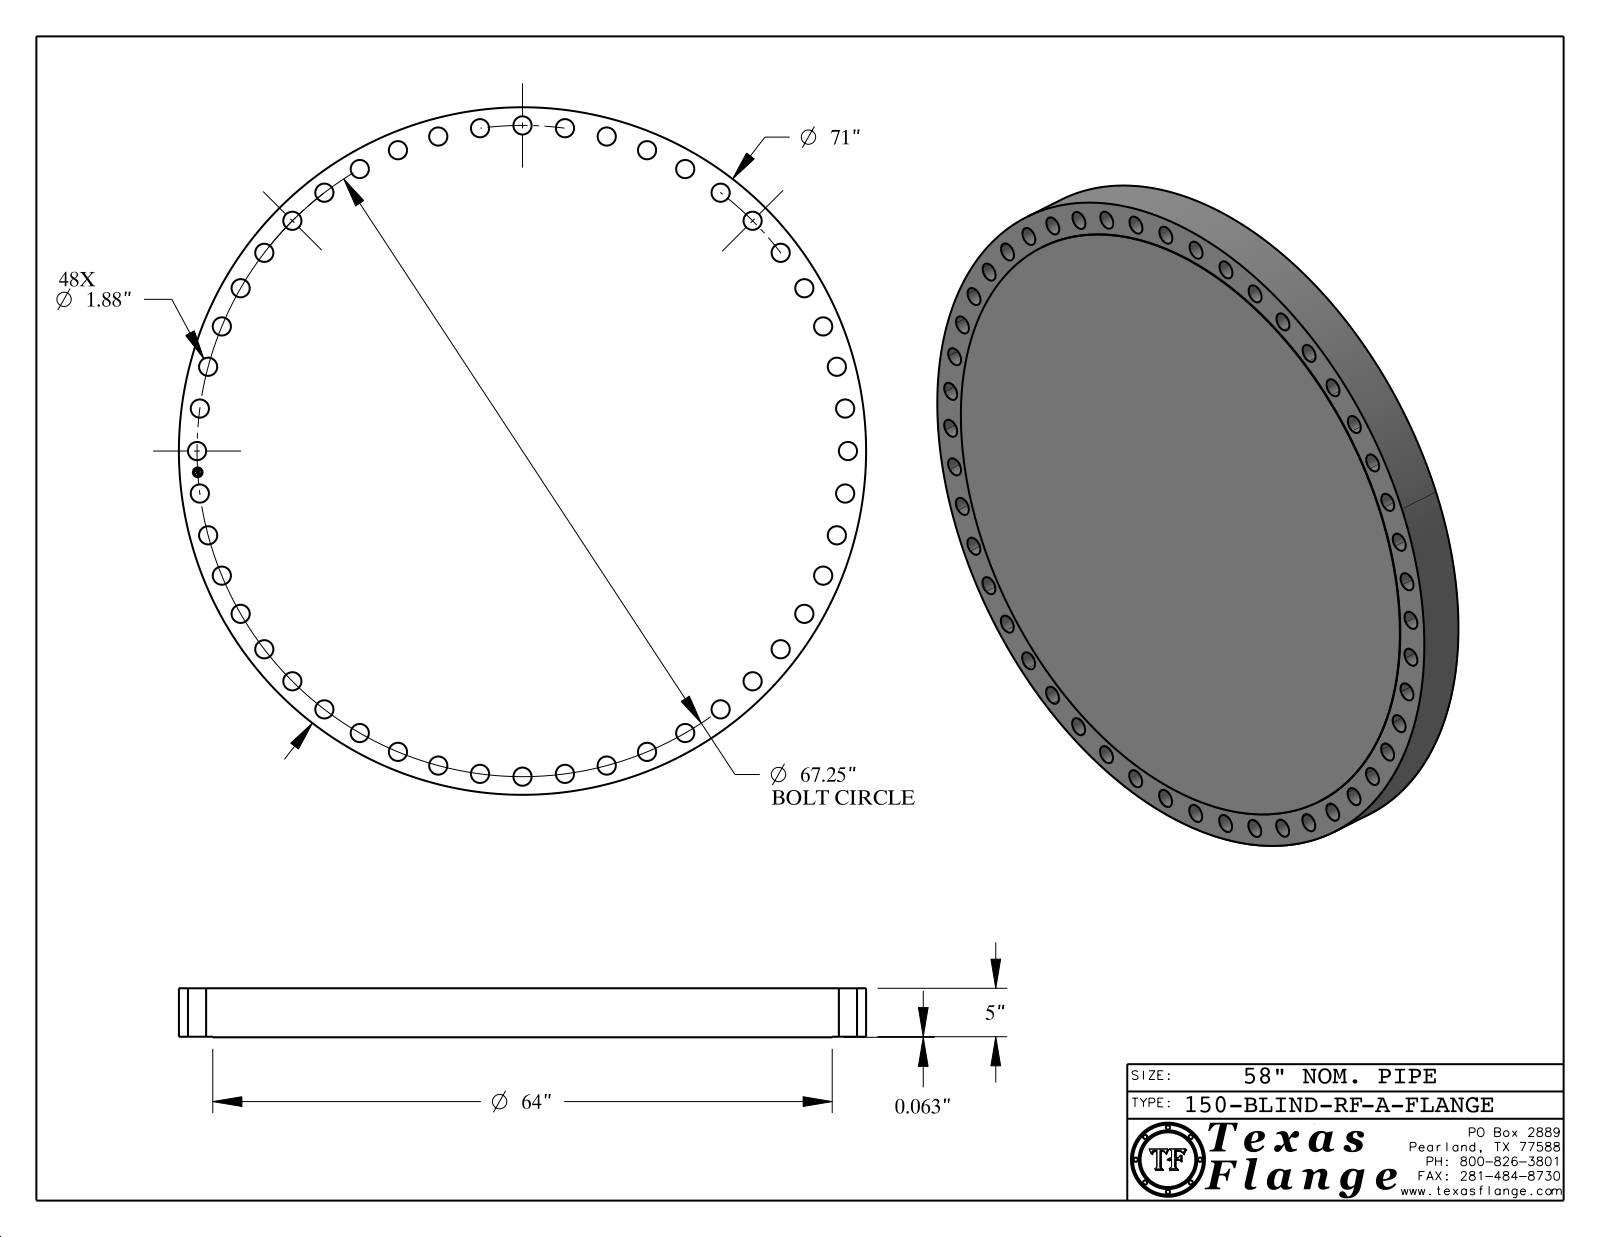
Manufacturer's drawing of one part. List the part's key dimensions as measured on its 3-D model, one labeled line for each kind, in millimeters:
Part name (STEP PRODUCT): 150-BLIND-RF, Series A
STEP written by: CATIA V5 STEP AP214 (AUTOMOTIVE_DESIGN)
Units: millimetres
Bodies: 1 solid, 488 faces (368 planar, 120 cylindrical, 0 other)
Overall size (bounding box): 1803.4 × 1803.4 × 128.6
Volume: 316 800 000 mm³ · Surface area: 6 579 000 mm²
Round holes (diameter × count): ⌀47.8 ×48, ⌀25.4 ×1
Round bosses / shafts (diameter × count): ⌀1.5 ×8, ⌀1803.4 ×1, ⌀1625.6 ×1, ⌀20 ×1
Main face-to-face distances: 128.6, 1.6, 127, 0.4, 128.2, 126.6, 7.6, 7.4, 0.5, 1.4
Hole centre spacings: 223, 111.7, 1704.5, 442.1, 653.7, 333.2, 1617.5, 1675.3
